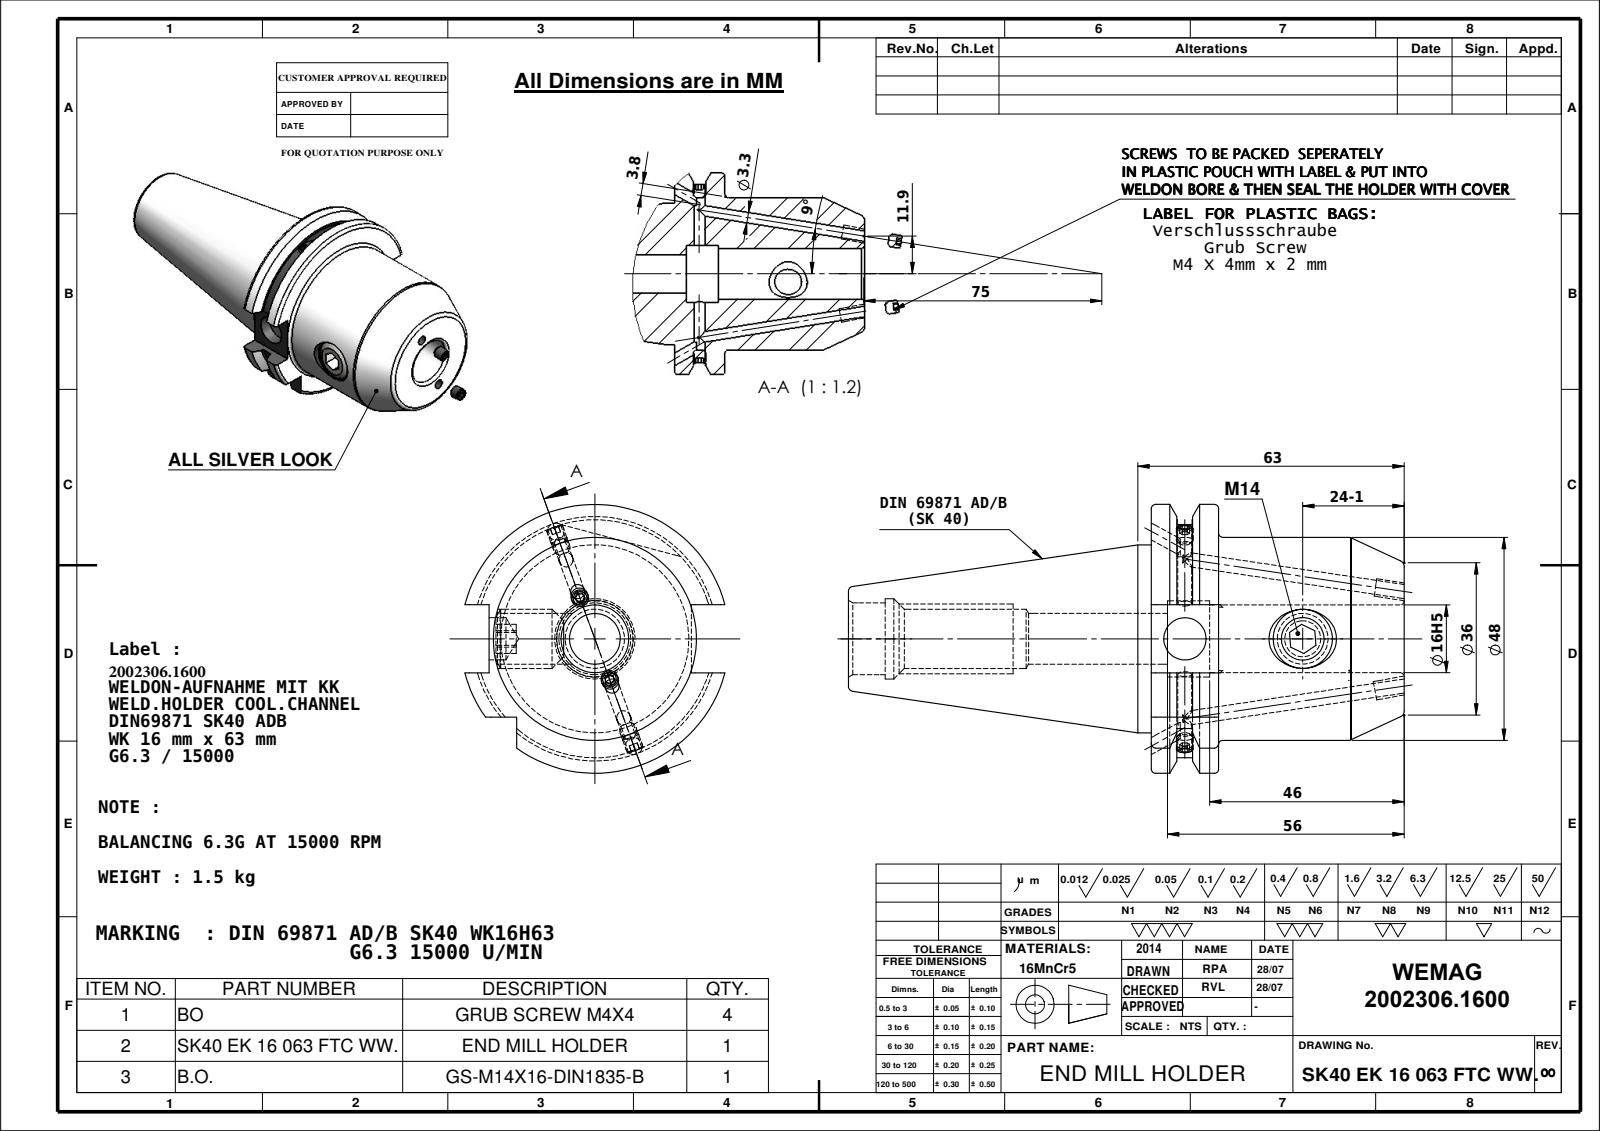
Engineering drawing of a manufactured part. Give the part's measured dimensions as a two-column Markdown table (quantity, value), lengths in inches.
| quantity | value |
| --- | --- |
| part name | Copy of M4X4_DIN 913 - M4 x 4-N; SK40 EK 16 063 FTC WW.; M14X16_ISO 4026 - M12 x 12-N |
| STEP written by | SolidWorks 2009 (CONFIG_CONTROL_DESIGN) |
| units | inches |
| bodies | 6 solids, 204 faces (80 planar, 58 cylindrical, 66 other) |
| overall size | 5.64 × 2.502 × 2.42 |
| volume | 9.958 in³ |
| surface area | 49.39 in² |
| round holes (diameter × count) | 0.13 × 3, 0.472 × 2, 0.551 × 2, 0.394 × 1, 0.63 × 1, 0.669 × 1, 0.709 × 1, 0.748 × 1 |
| round bosses / shafts (diameter × count) | 0.157 × 4, 1.89 × 1, 1.75 × 1 |
| partial cylindrical surfaces (radius × count) | 1.107 × 1, 1.251 × 1 |
| main face-to-face distances | 0.626, 2.354, 1.728, 0.634, 1.882, 0.15, 0.476, 2.205, 2.819, 2.969 |
| hole center spacings | 1.096 |
